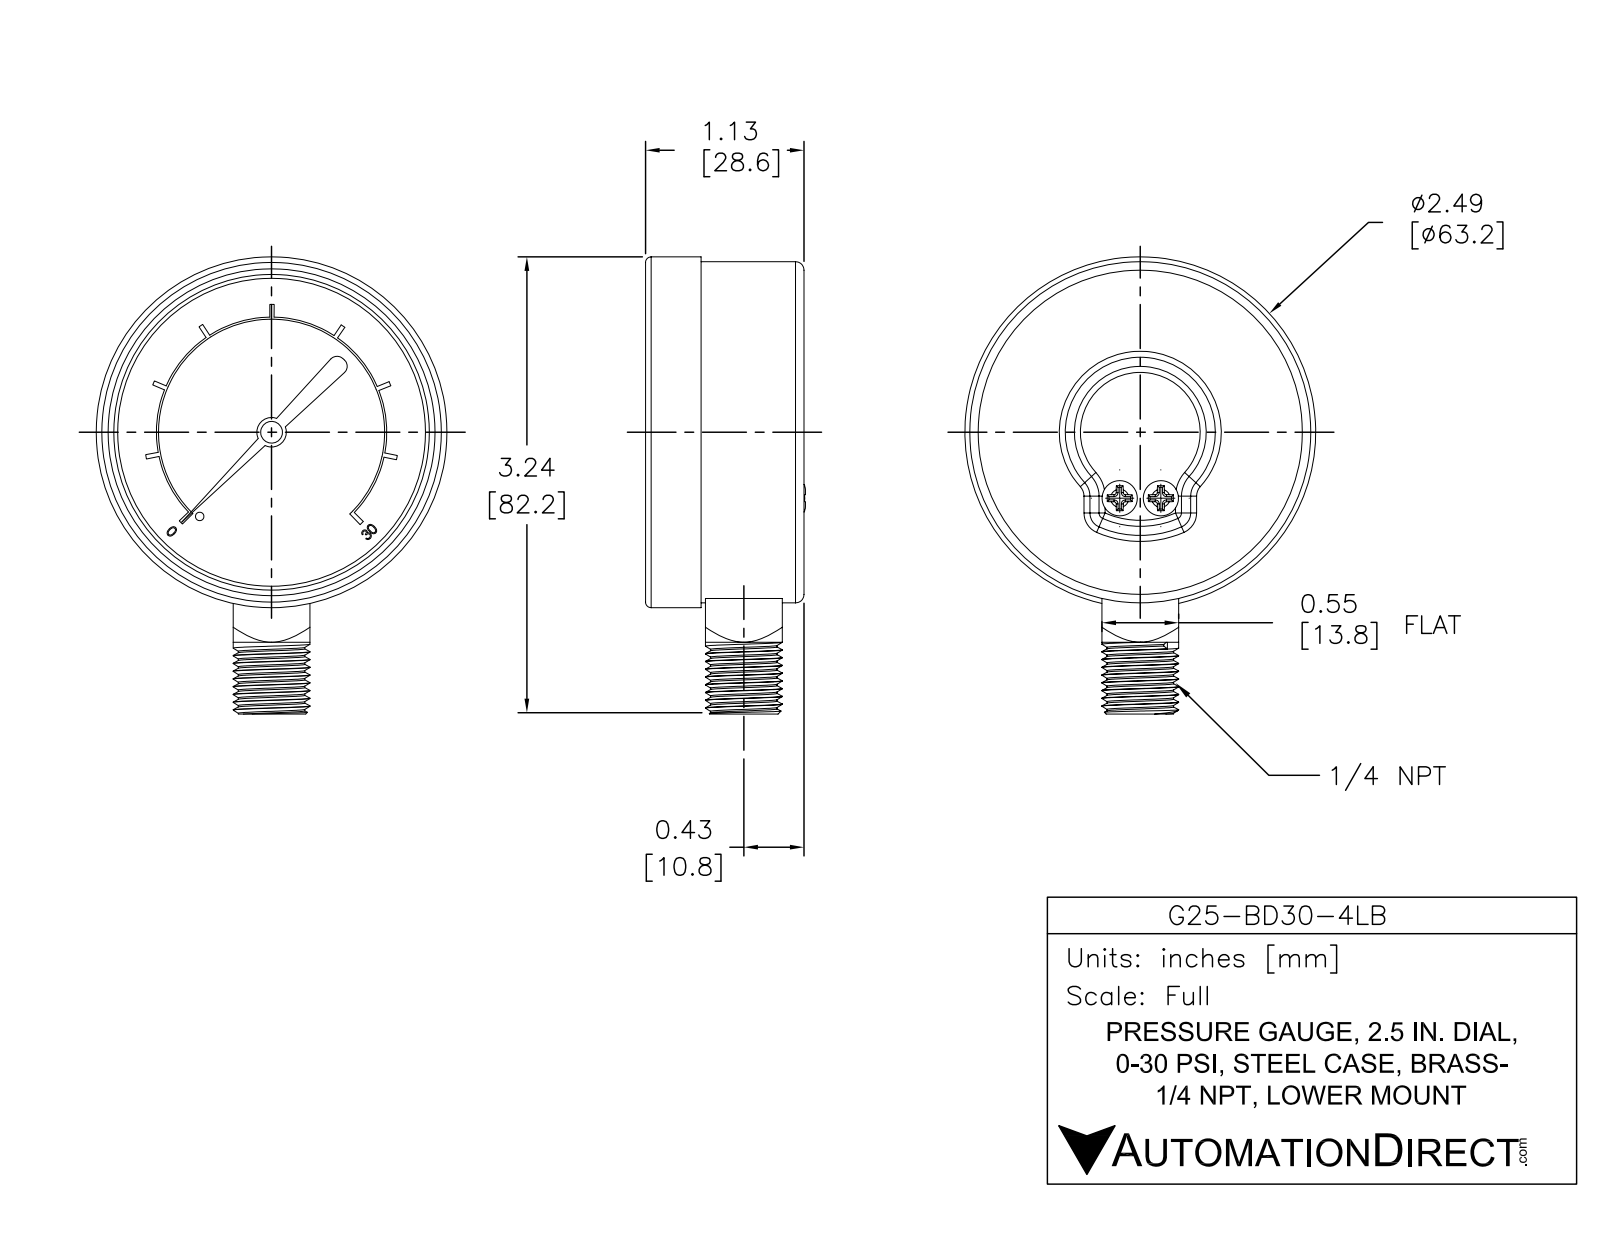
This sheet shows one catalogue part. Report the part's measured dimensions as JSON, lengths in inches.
{"part_name": "G25-BD30-4LB", "step_written_by": "SolidWorks 2021 (AUTOMOTIVE_DESIGN)", "units": "inches", "bodies": {"solids": 1, "faces": 214, "planar": 110, "cylindrical": 35, "other": 69}, "overall_size": [3.245, 2.49, 1.135], "volume_in3": 4.288, "surface_area_in2": 22.39, "round_holes": [[0.14, 1], [2.185, 1]], "round_bosses_or_shafts": [[0.25, 2], [2.49, 1], [2.421, 1], [0.545, 1], [0.154, 1], [0.123, 1], [0.06, 1]], "partial_cylinders_radius": [[0.06, 6], [0.105, 1], [0.803, 1], [0.818, 1]], "face_to_face_distances": [0.835, 0.1, 0.735, 1.125, 1.025, 0.29, 0.545, 0.731, 0.631, 0.104]}
